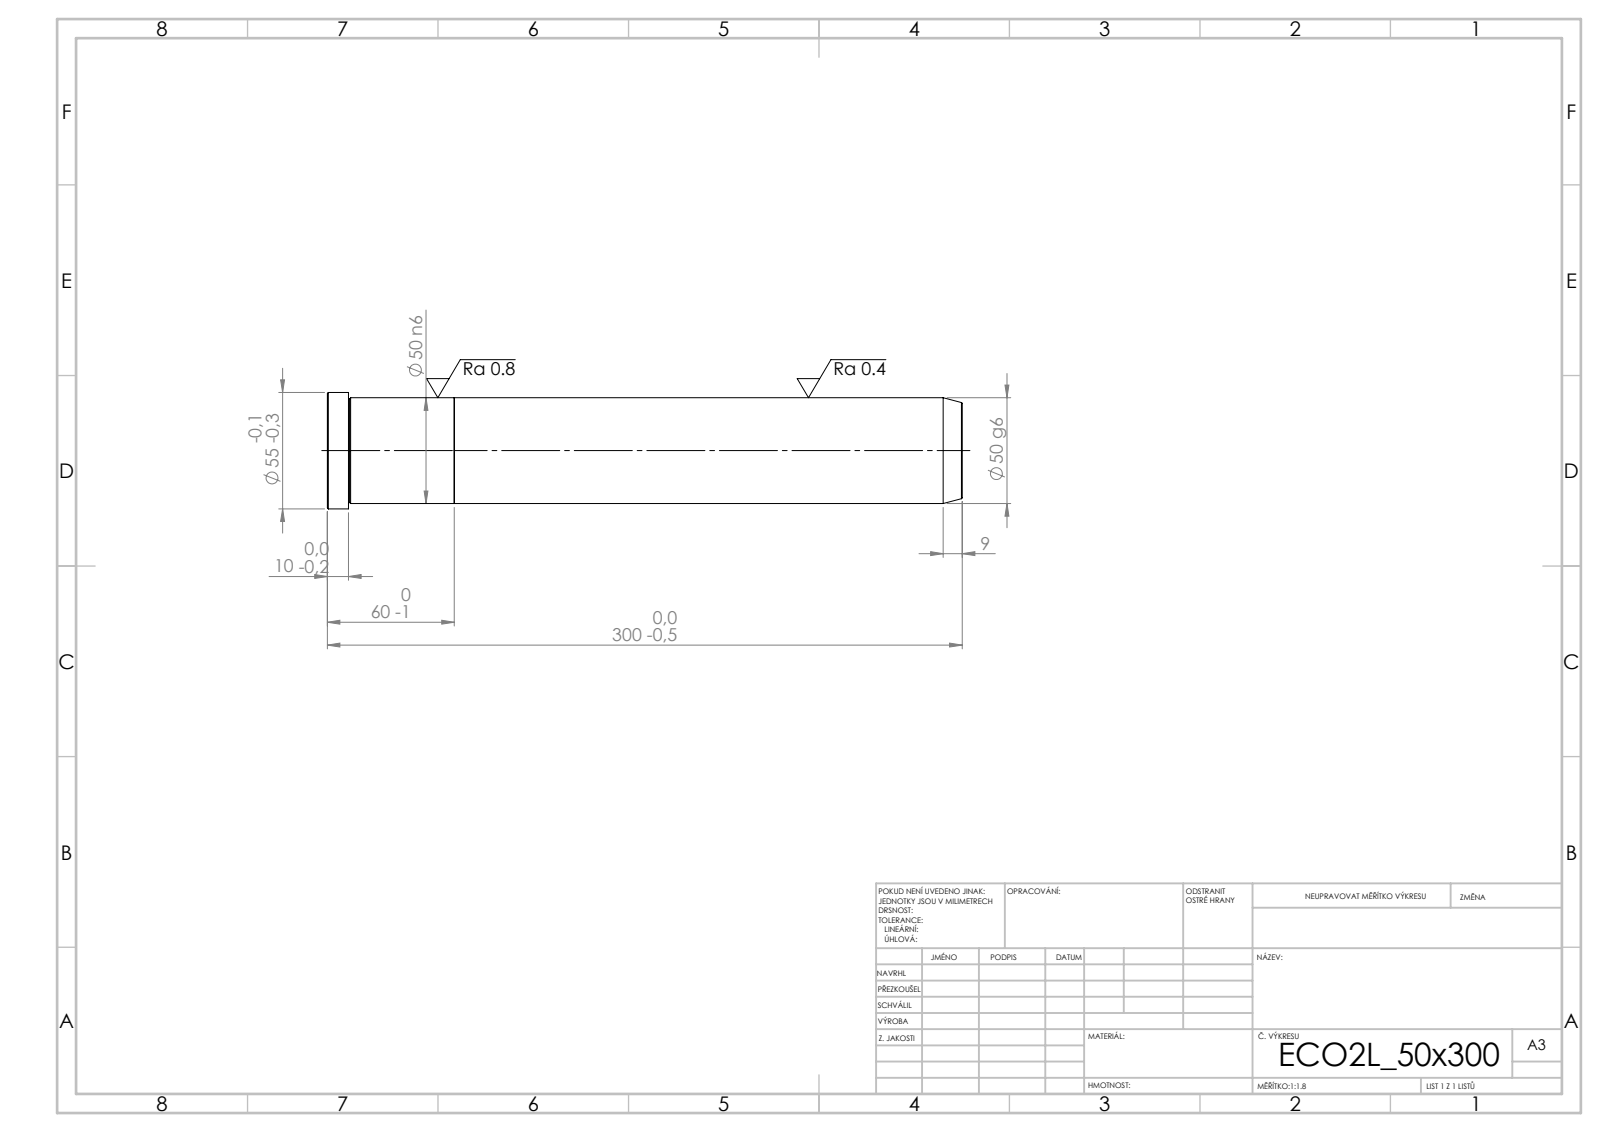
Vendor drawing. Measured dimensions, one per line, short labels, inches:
written by: SolidWorks 2019 (CONFIG_CONTROL_DESIGN)
unit: in
bodies: 2 solids, 21 faces (5 planar, 6 cylindrical, 10 other)
size: 11.811 × 2.165 × 2.165
volume: 36.09 in³; area: 86.18 in²
bosses: 1× ⌀2.165, 1× ⌀1.969
face distances: 2.362, 9.449, 11.811, 11.417, 1.969, 0.394
